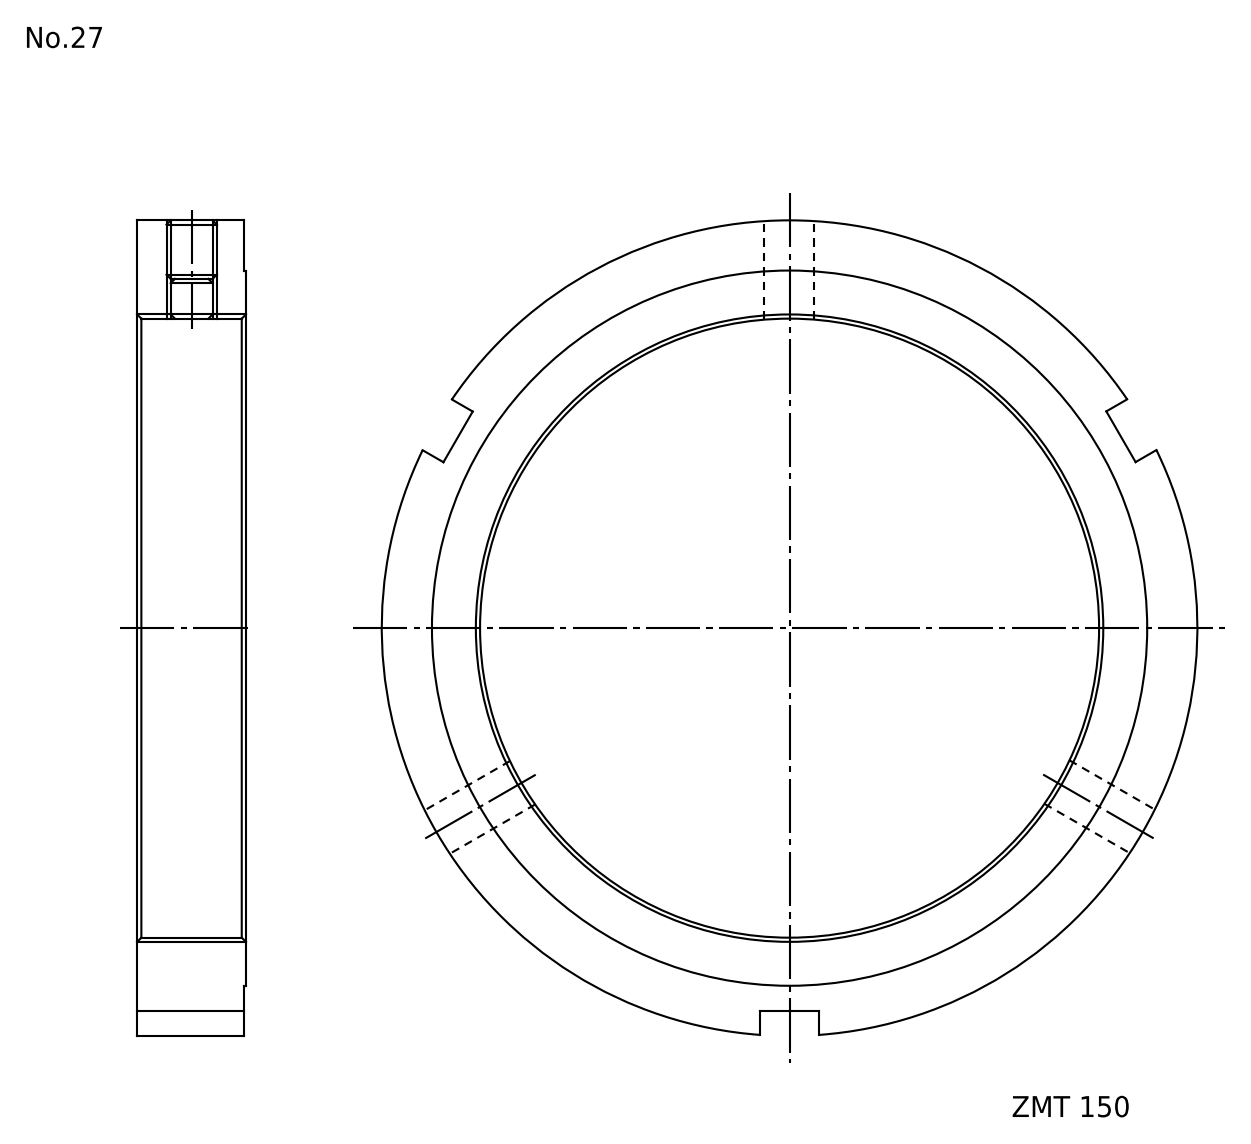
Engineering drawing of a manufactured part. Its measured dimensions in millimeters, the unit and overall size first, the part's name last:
Units: millimetres
Overall size (bounding box): 195 × 194.75 × 26
Round holes (diameter × count): ⌀10.11 ×3, ⌀150 ×1
Round bosses / shafts (diameter × count): ⌀195 ×1, ⌀171 ×1
Main face-to-face distances: 25.5, 0.5, 26, 14
Volume: 301 826 mm³ · Surface area: 54 574 mm²
Bodies: 1 solid, 20 faces (12 planar, 8 cylindrical, 0 other)
Part name (STEP PRODUCT): FKD ZMT150
STEP written by: Autodesk Inventor 2011 (AUTOMOTIVE_DESIGN)
